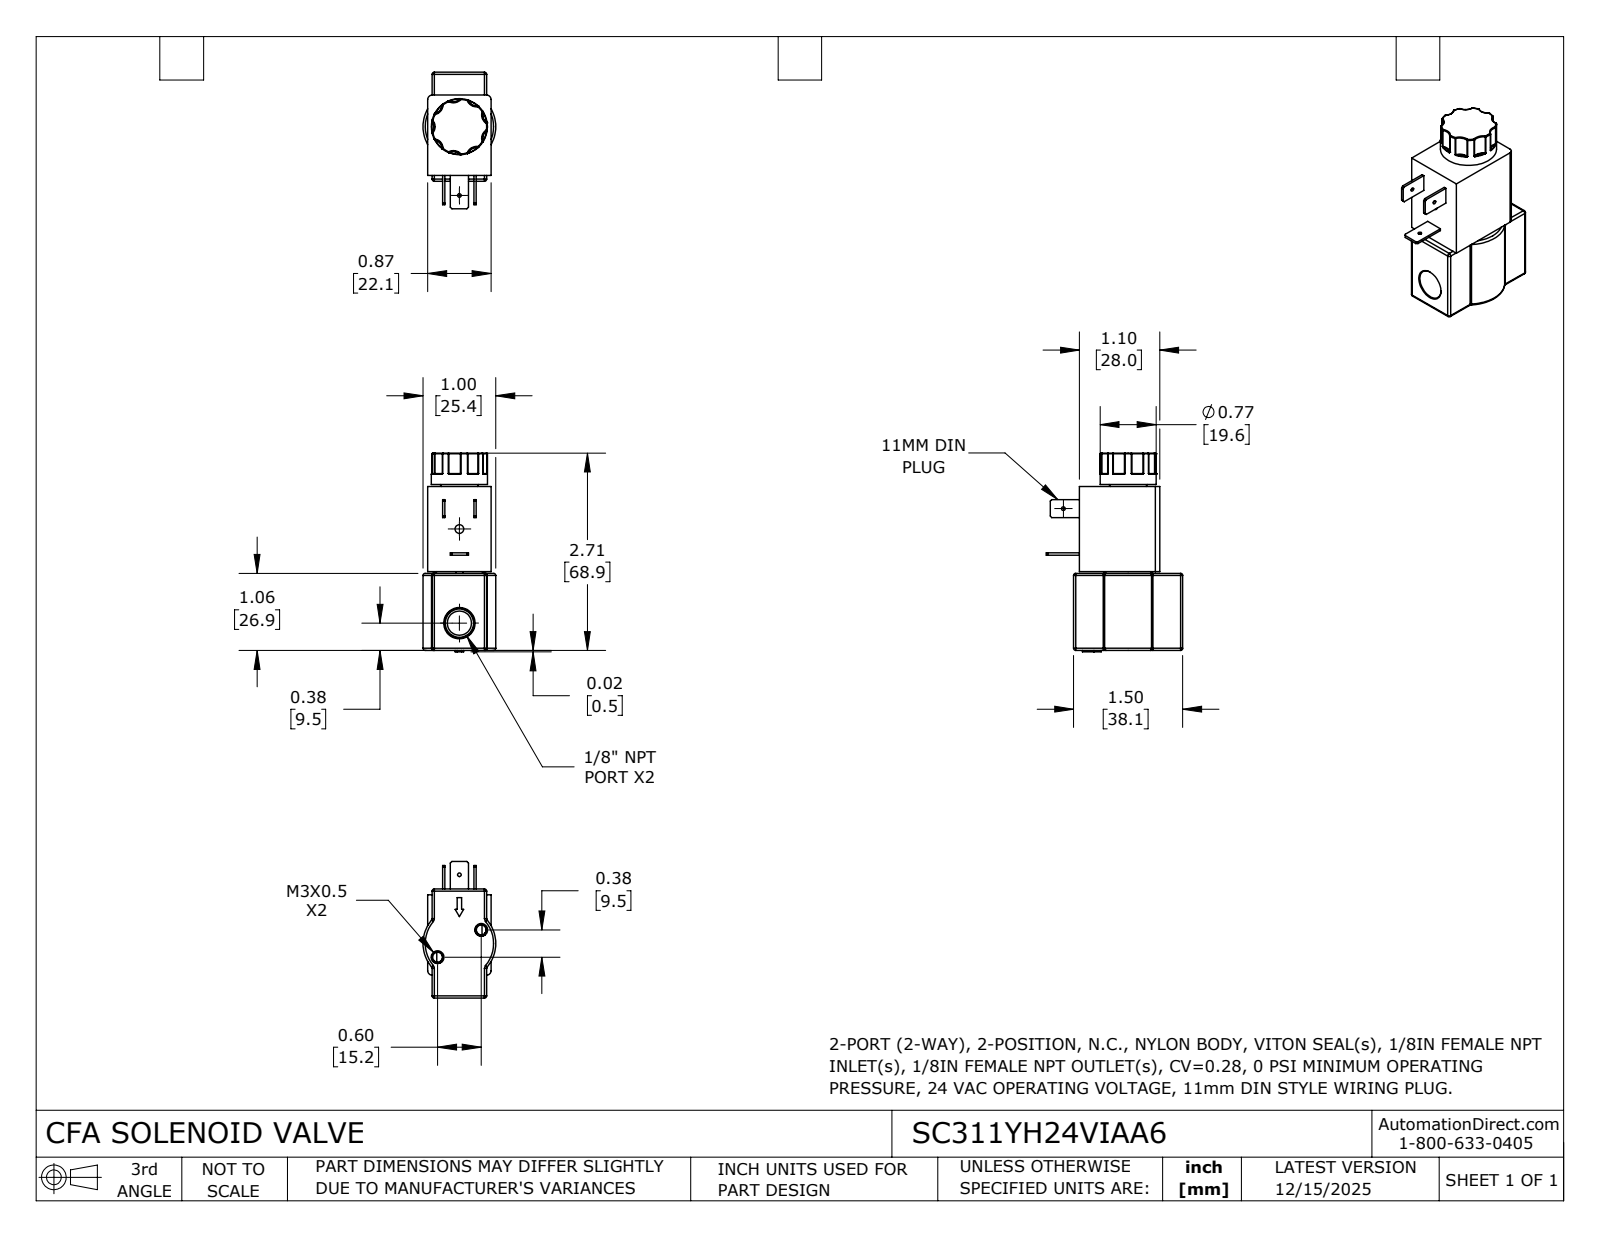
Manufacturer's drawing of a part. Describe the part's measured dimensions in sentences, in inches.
The part is named "SC311YH24VIAA6". Its 3-D file was written by "SolidWorks 2024 (CONFIG_CONTROL_DESIGN)". It is 1 solid with 383 faces: 62 planar, 117 cylindrical and 204 other. Overall it measures 2.732 by 1.877 by 1 inches. Its volume is 2.516 cubic inches and its surface area 17.12 square inches. Round holes: 2 of diameter 0.05, 2 of diameter 0.136, 1 of diameter 0.12, 1 of diameter 0.332. Round bosses or shafts: 1 of diameter 0.77. Partial cylindrical surfaces (rounded edges, fillets, slot ends): 18 of radius 0.01, 16 of radius 0.03, 7 of radius 0.133, 2 of radius 0.06, 2 of radius 0.132, 2 of radius 0.295, 1 of radius 0.311, 1 of radius 0.5. The main face-to-face distances are 0.06, 0.81, 0.87, 1.104, 2.252, 1.06, 1.192, 0.75, 1.085, 0.025. The hole center spacings are 0.707, 0.815, 1.172, 1.293.
